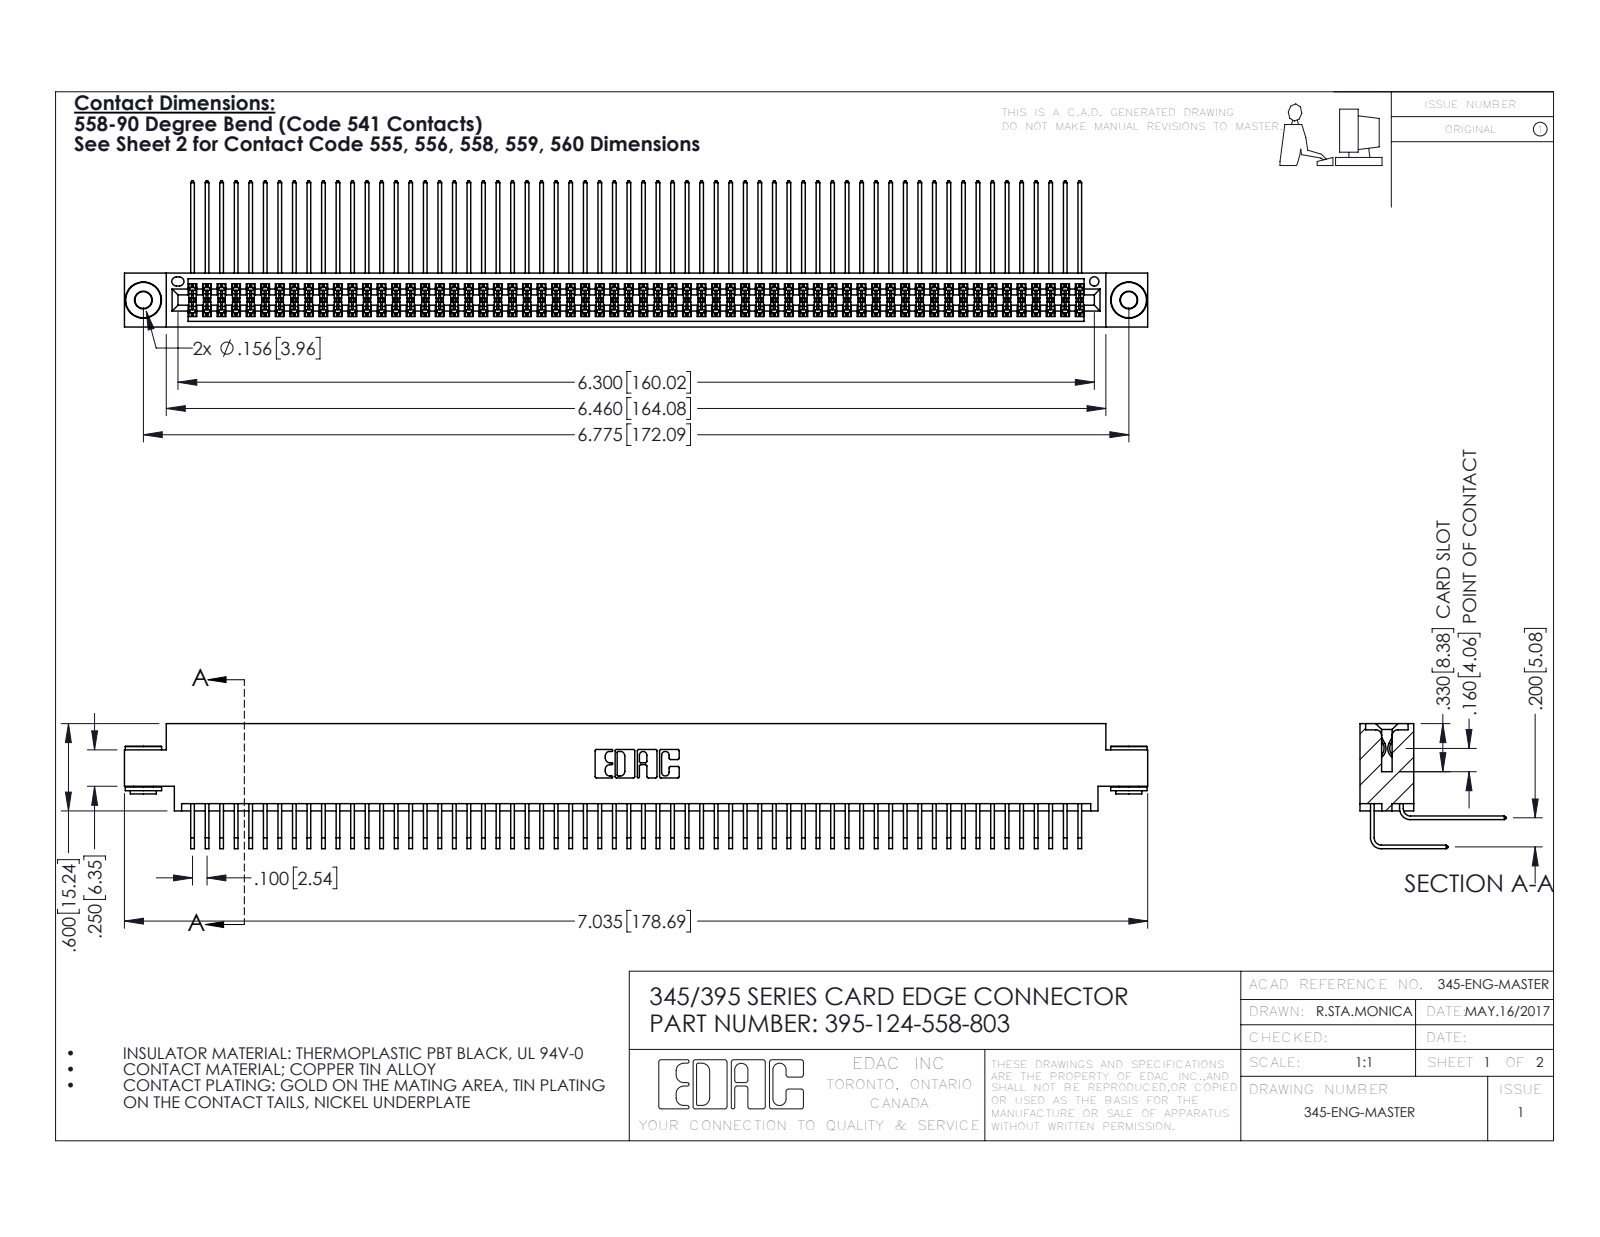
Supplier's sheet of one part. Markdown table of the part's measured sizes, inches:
| quantity | value |
| --- | --- |
| part name | 345-292-001_558 Tail - 2; 345-250-002_345-250-002-102; 395-124-558-803; 345-292-001_558 559 Tail - 1 (+1 more) |
| STEP written by | SolidWorks 2016 (CONFIG_CONTROL_DESIGN) |
| units | inches |
| bodies | 127 solids, 6616 faces (4434 planar, 2174 cylindrical, 8 other) |
| overall size | 7.035 × 1.005 × 0.859 |
| volume | 1.108 in³ |
| surface area | 47.97 in² |
| round holes (diameter × count) | 0.116 × 2, 0.156 × 2, 0.064 × 1 |
| round bosses / shafts (diameter × count) | 0.25 × 2, 0.18 × 2, 0.136 × 2 |
| partial cylindrical surfaces (radius × count) | 0.006 × 187, 0.01 × 22, 0.007 × 6, 0.031 × 6, 0.026 × 3, 0.014 × 2, 0.019 × 2, 0.022 × 2 |
| main face-to-face distances | 0.072, 0.298, 0.2, 0.37, 0.098, 0.272, 0.025, 0.225, 0.175, 0.025 |
| hole center spacings | 0.27, 6.539, 6.775 |
